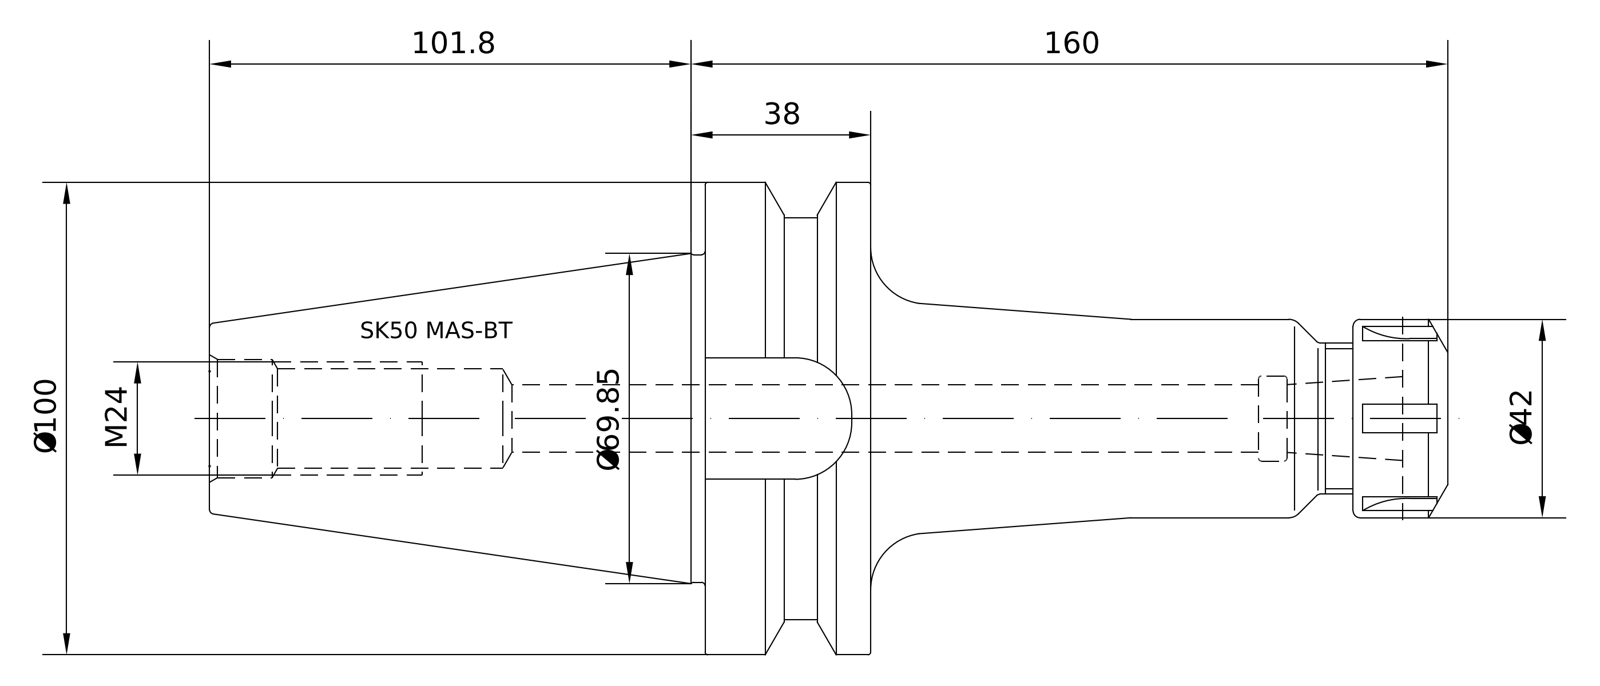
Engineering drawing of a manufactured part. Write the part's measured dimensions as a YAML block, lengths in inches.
part_name: "50-522-25; 83-912-25; 50-522-25_ASM"
step_written_by: "PRO/ENGINEER BY PARAMETRIC TECHNOLOGY CORPORATION, 2010430 (CONFIG_CONTROL_DESIGN)"
units: inches
bodies: {solids: 2, faces: 148, planar: 46, cylindrical: 26, other: 76}
overall_size: [10.307, 3.936, 3.936]
volume: 38.95
surface_area: 112.5
round_holes:
  - {diameter: 0.709, count: 1}
  - {diameter: 0.817, count: 1}
  - {diameter: 0.985, count: 1}
  - {diameter: 1.012, count: 1}
round_bosses_or_shafts:
  - {diameter: 3.936, count: 1}
  - {diameter: 3.337, count: 1}
  - {diameter: 2.722, count: 1}
  - {diameter: 1.654, count: 1}
  - {diameter: 1.26, count: 1}
  - {diameter: 0.945, count: 1}
partial_cylinders:
  - {radius: 0.508, count: 1}
face_to_face_distances: [1.378, 5.394, 4.016, 2.772, 6.181, 4.803, 0.787, 4.126, 5.504, 9.52]
